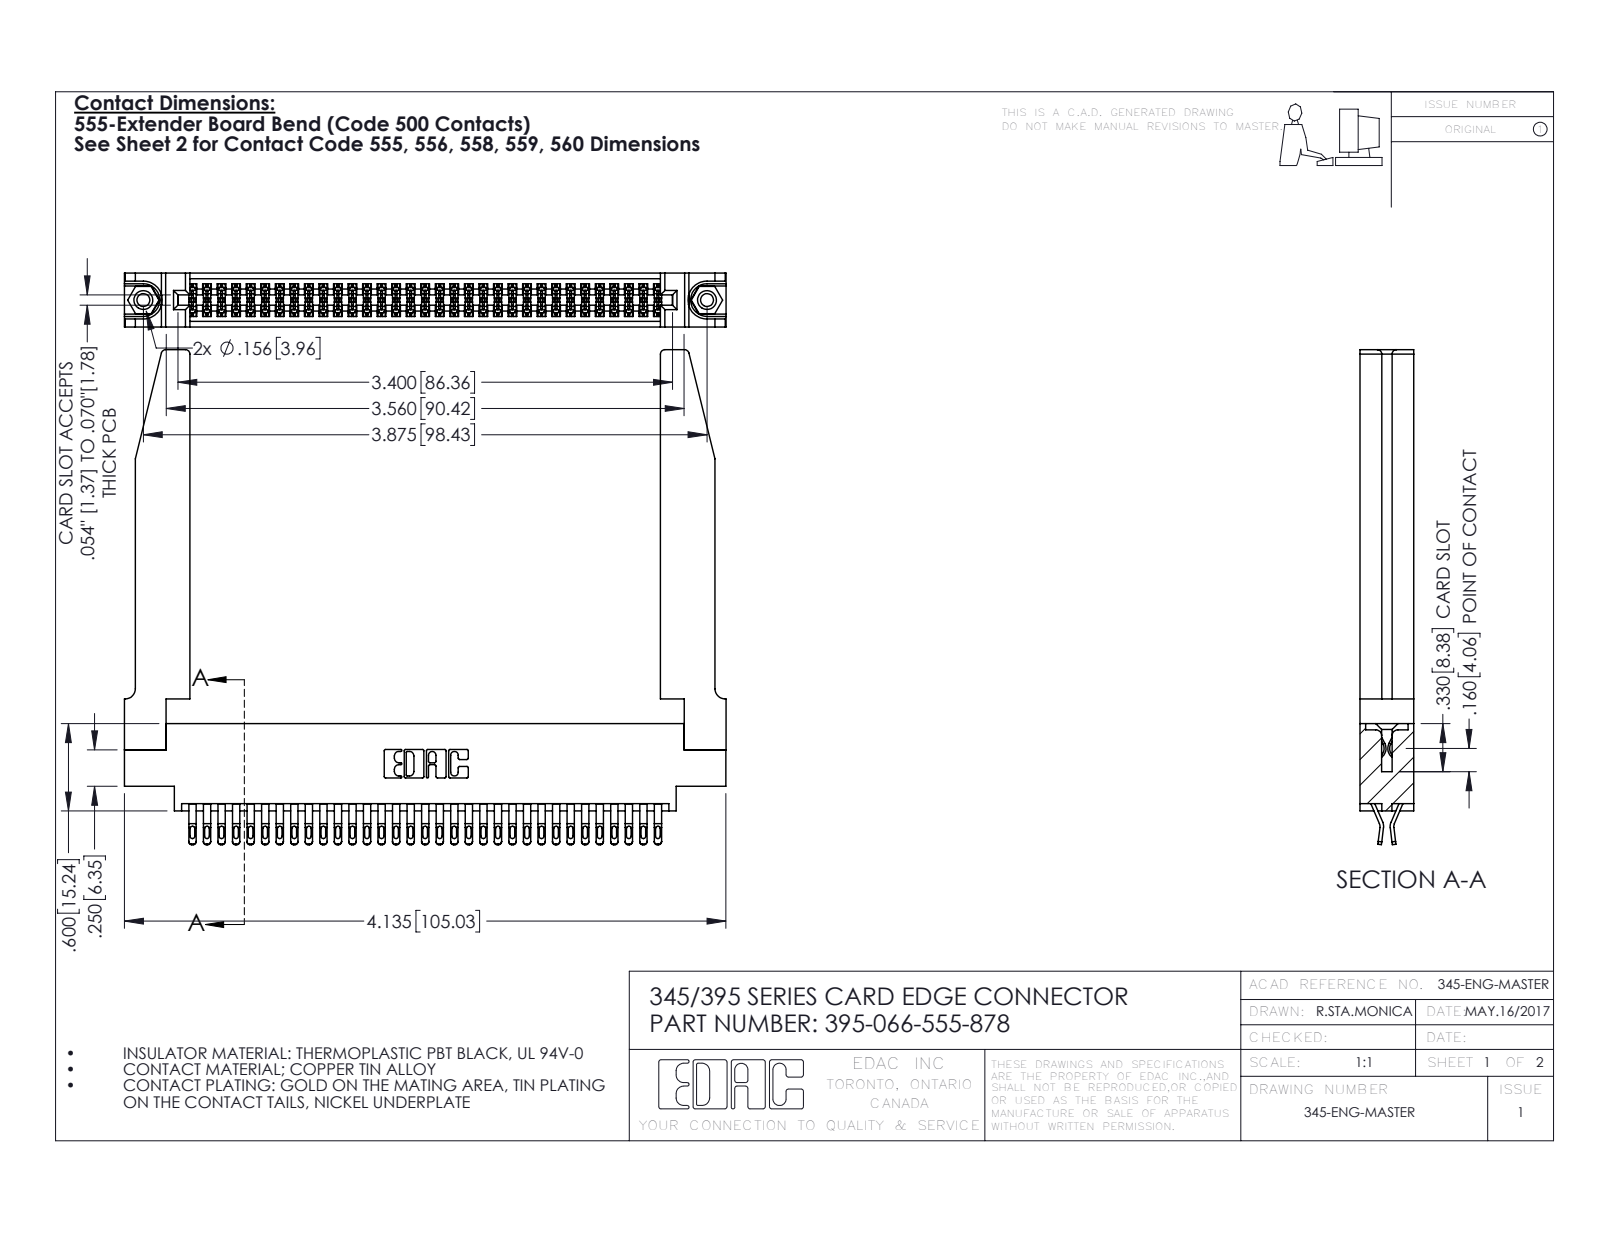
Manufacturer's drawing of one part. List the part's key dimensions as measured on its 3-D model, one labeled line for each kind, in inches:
Part name (STEP PRODUCT): 395-066-555-878; 345-292-001_555 Tail; 345 Part_0.170 Offset - 0.156 Dia-TH; 345-250-001_345-250-001-102 (+1 more)
STEP written by: SolidWorks 2016 (CONFIG_CONTROL_DESIGN)
Units: inches
Bodies: 71 solids, 4060 faces (2272 planar, 1736 cylindrical, 52 other)
Overall size (bounding box): 4.136 × 3.402 × 0.37
Volume: 1.097 in³ · Surface area: 34.95 in²
Round holes (diameter × count): ⌀0.089 ×2, ⌀0.125 ×2, ⌀0.156 ×2, ⌀0.064 ×1
Round bosses / shafts (diameter × count): ⌀0.155 ×2
Partial cylindrical surfaces — rounded edges, fillets, slot ends (radius × count): R0.016 ×165, R0.02 ×132, R0.006 ×99, R0.01 ×22, R0.03 ×8, R0.007 ×6, R0.031 ×6, R0.026 ×3
Main face-to-face distances: 0.37, 0.072, 0.298, 0.025, 0.098, 0.272, 0.2, 0.225, 0.148, 0.15
Hole centre spacings: 0.27, 3.64, 3.875
